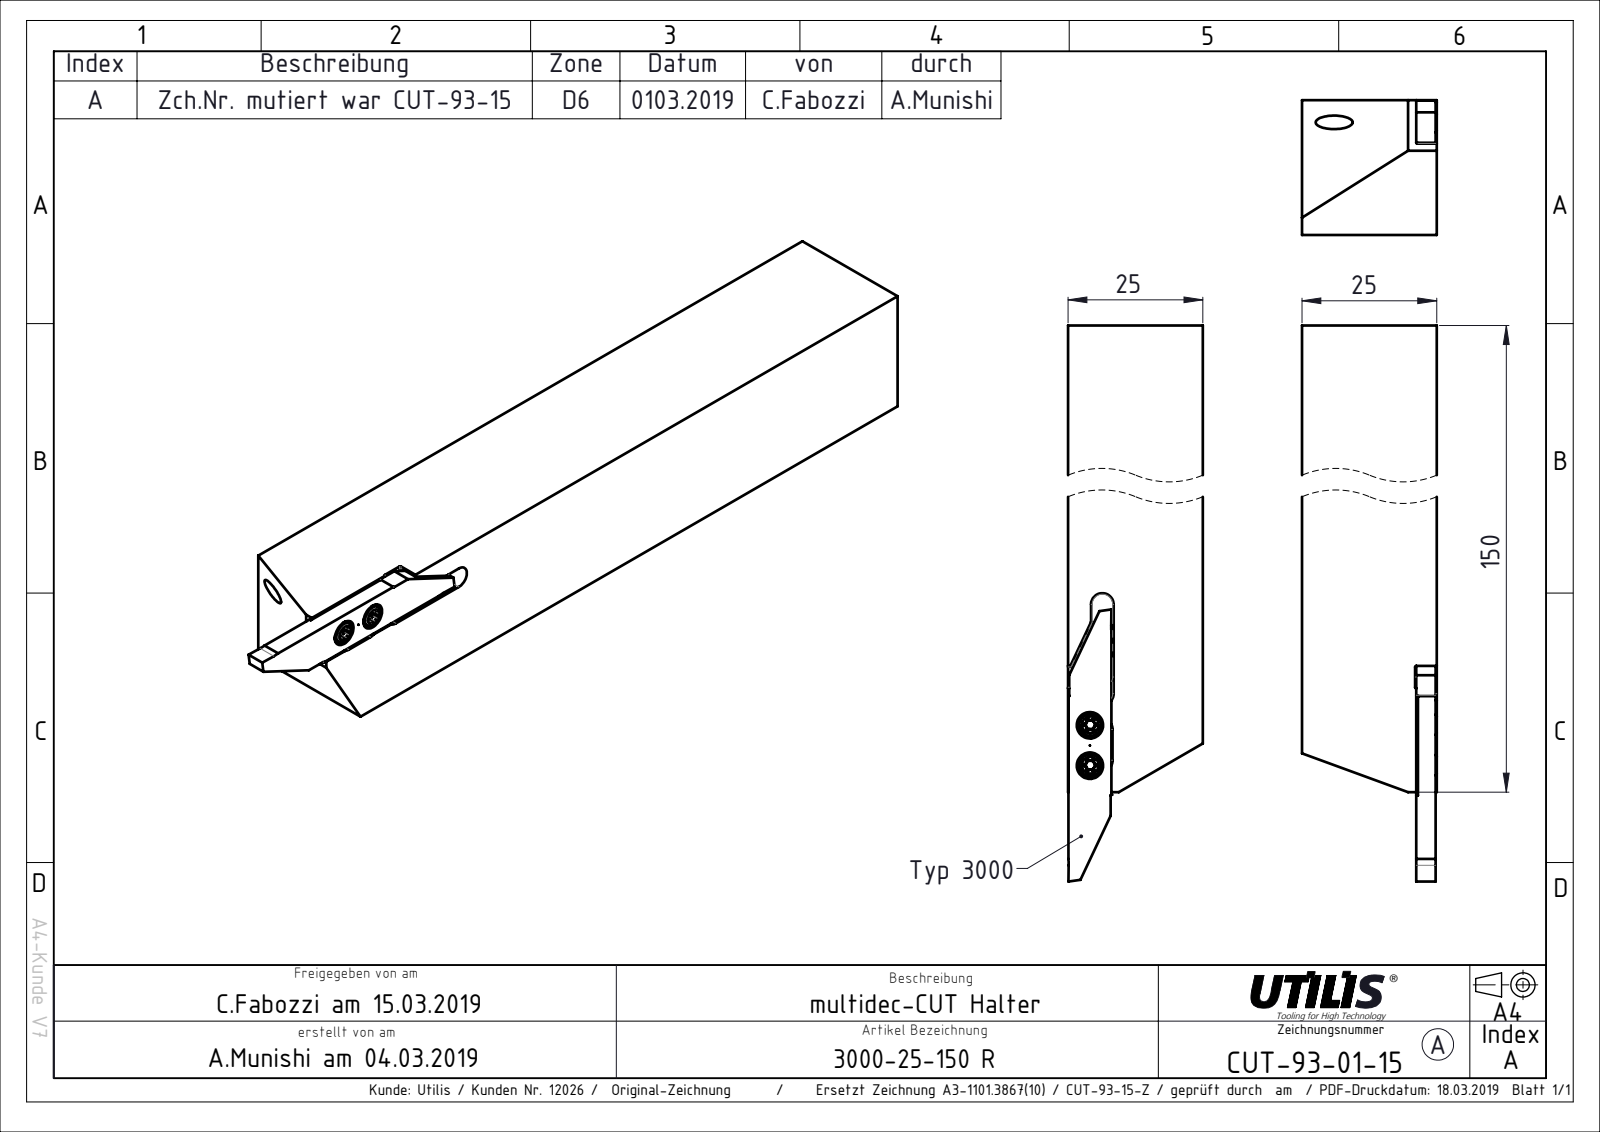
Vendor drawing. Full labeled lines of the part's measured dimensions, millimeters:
Part name (STEP PRODUCT): CUT-93-15
STEP written by: SolidWorks 2016 (AUTOMOTIVE_DESIGN)
Units: millimetres
Bodies: 1 solid, 45 faces (36 planar, 9 cylindrical, 0 other)
Overall size (bounding box): 166.5 × 25 × 25
Volume: 91 217 mm³ · Surface area: 16 440 mm²
Partial cylindrical surfaces — rounded edges, fillets, slot ends (radius × count): R2.1 ×4, R0.15 ×2, R10 ×2
Main face-to-face distances: 25, 24.8, 3.6, 3.8, 21.2, 17, 8, 16.55, 0.45, 8.45
